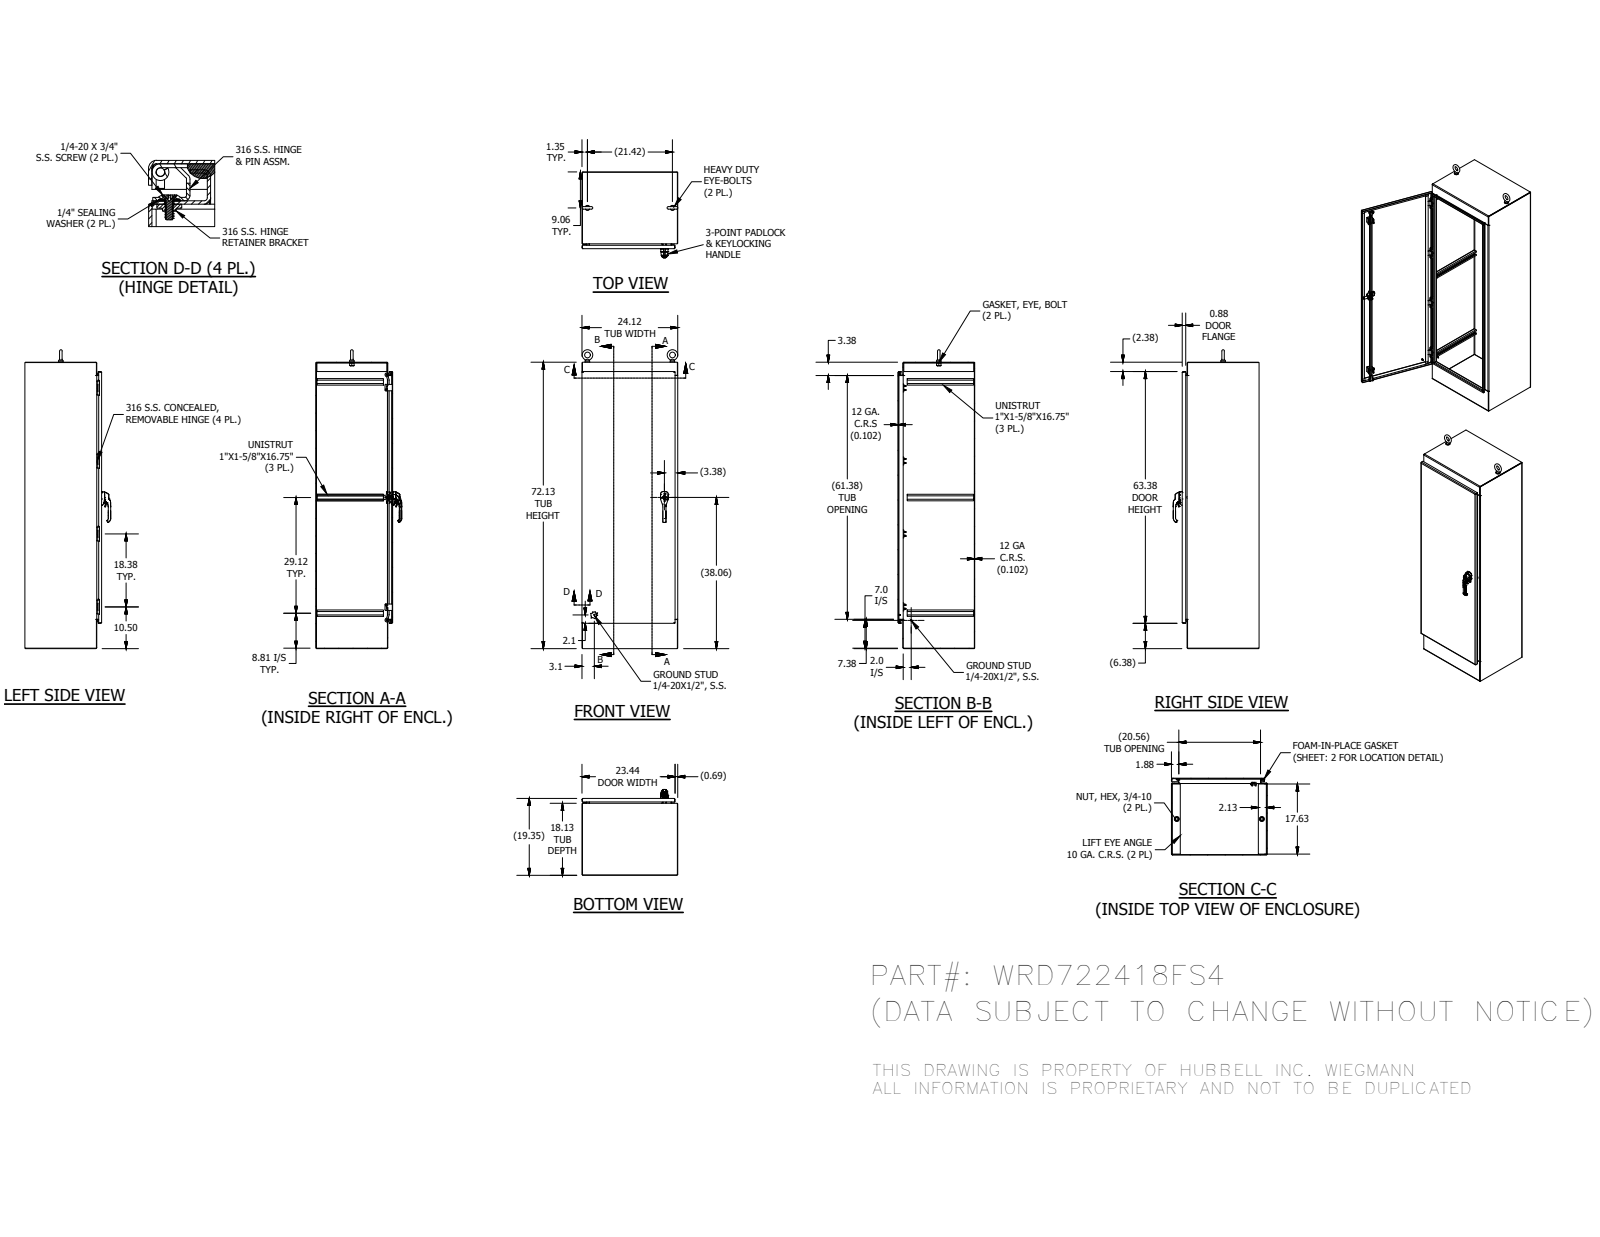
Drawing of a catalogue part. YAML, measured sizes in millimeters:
part_name: "WRD722418FS4BLR; WRD2418FS4TOP; WRD2418FS4BTM; WRD7224FS4DR (+8 more)"
step_written_by: "Autodesk Inventor 2016 (AUTOMOTIVE_DESIGN)"
units: millimeters
bodies: {solids: 85, faces: 3586, planar: 1457, cylindrical: 1207, other: 922}
overall_size: [1911.29, 612.83, 549.04]
volume: 14770000
surface_area: 11080000
round_holes:
  - {diameter: 5.84, count: 8}
  - {diameter: 7.02, count: 8}
  - {diameter: 7.14, count: 8}
  - {diameter: 16.51, count: 8}
  - {diameter: 5.08, count: 4}
  - {diameter: 5.4, count: 3}
  - {diameter: 6, count: 3}
  - {diameter: 7.11, count: 3}
  - {diameter: 6.13, count: 2}
  - {diameter: 6.35, count: 2}
  - {diameter: 6.41, count: 2}
  - {diameter: 10.16, count: 2}
round_bosses_or_shafts:
  - {diameter: 6.35, count: 15}
  - {diameter: 15.88, count: 8}
  - {diameter: 10.25, count: 8}
  - {diameter: 4.63, count: 8}
  - {diameter: 31.75, count: 2}
  - {diameter: 28.45, count: 2}
  - {diameter: 25.4, count: 2}
  - {diameter: 19.05, count: 2}
partial_cylinders:
  - {radius: 0.5, count: 165}
  - {radius: 0.3, count: 84}
  - {radius: 1.59, count: 27}
  - {radius: 0.25, count: 24}
  - {radius: 3.17, count: 20}
  - {radius: 0.47, count: 19}
  - {radius: 2, count: 15}
  - {radius: 1.27, count: 14}
face_to_face_distances: [2.59, 488.83, 610.19, 486.24, 491.42, 607.6, 612.78, 1829.39, 457.79, 31.04]
hole_center_spacings: [12.5, 25.4, 466.73, 933.45, 6.5, 22.5, 51.5, 6]
